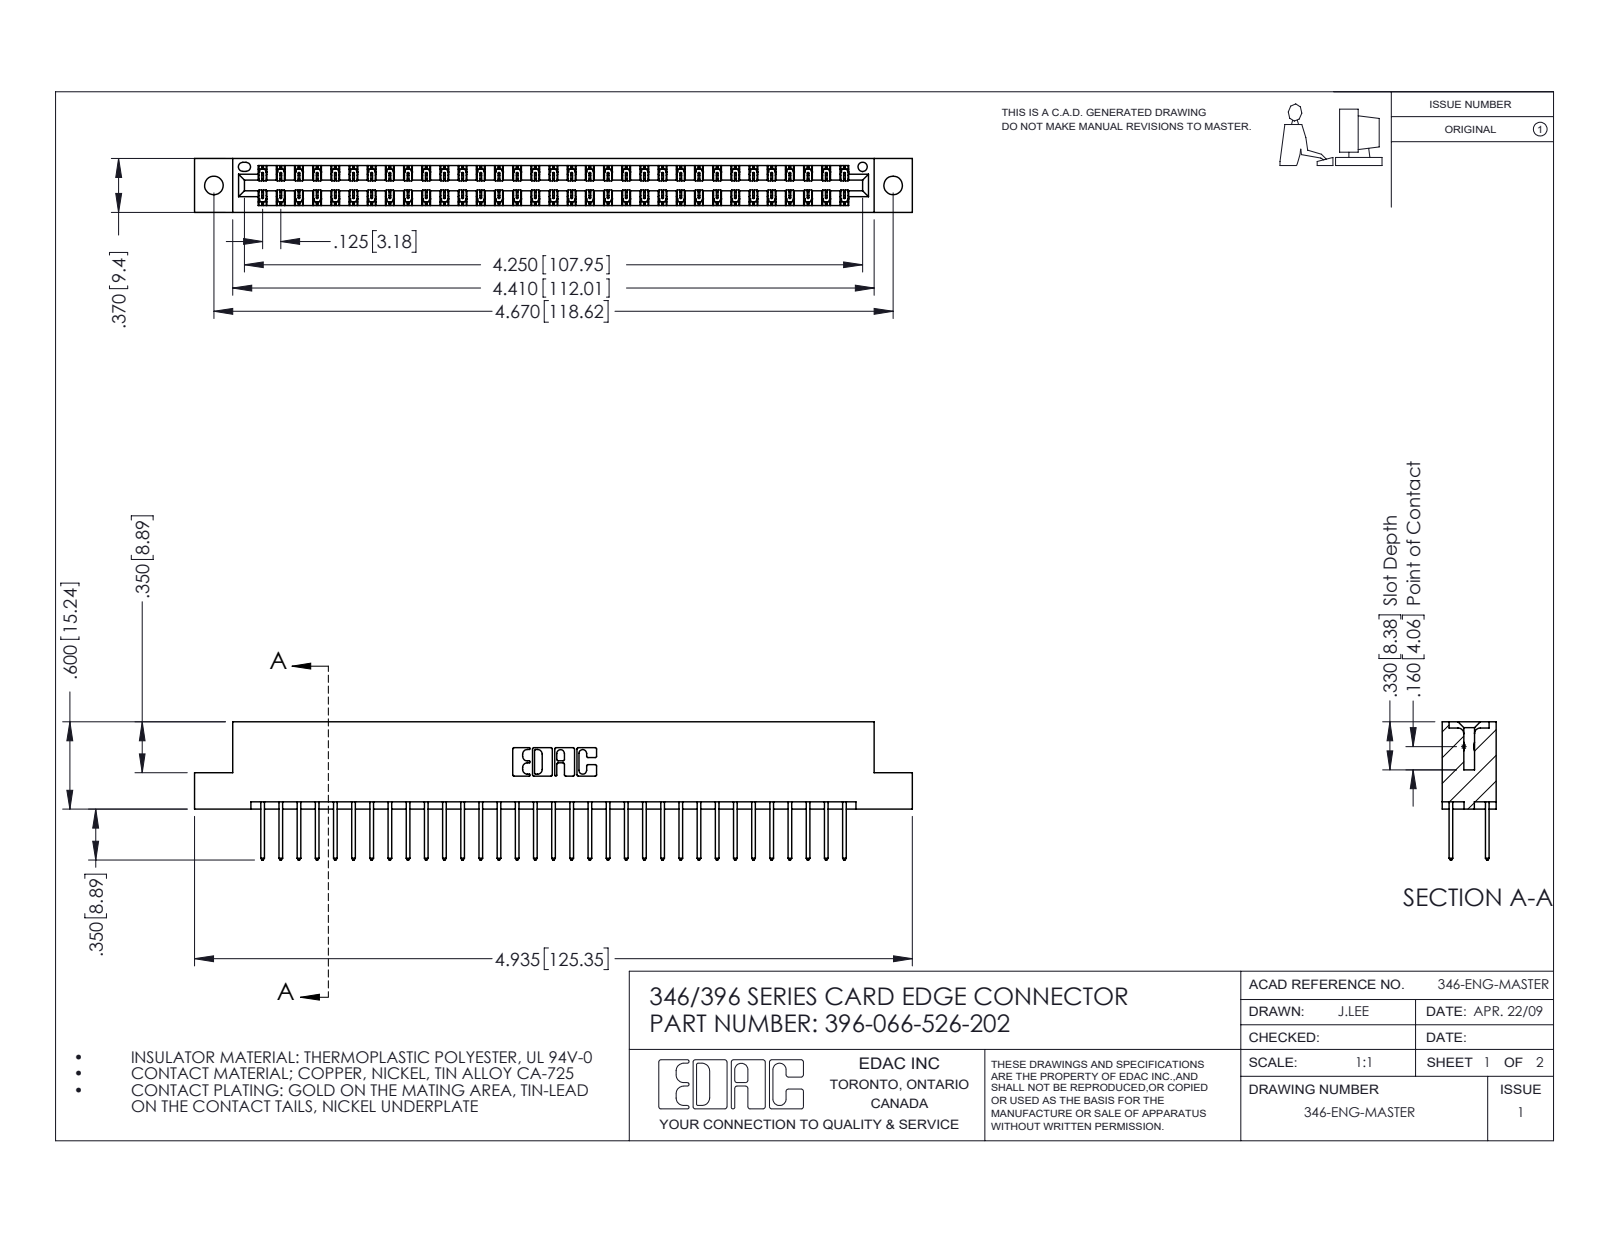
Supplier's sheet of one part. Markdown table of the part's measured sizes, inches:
| quantity | value |
| --- | --- |
| part name | 346 Part_Flush Mounting Lugs - 0.128 Dia; 396-066-526-202; 345-292-001_345-293-126 |
| STEP written by | SolidWorks 2016 (CONFIG_CONTROL_DESIGN) |
| units | inches |
| bodies | 67 solids, 3554 faces (2386 planar, 1168 cylindrical, 0 other) |
| overall size | 4.935 × 0.95 × 0.37 |
| volume | 0.746 in³ |
| surface area | 26.16 in² |
| round holes (diameter × count) | 0.128 × 2, 0.064 × 1 |
| partial cylindrical surfaces (radius × count) | 0.006 × 99, 0.01 × 66, 0.01 × 22, 0.007 × 6, 0.031 × 6, 0.026 × 3, 0.014 × 2, 0.022 × 2 |
| main face-to-face distances | 0.048, 0.322, 0.25, 0.37, 0.072, 0.298, 0.025, 0.275, 0.148, 0.222 |
| hole center spacings | 0.246, 4.462, 4.67 |
